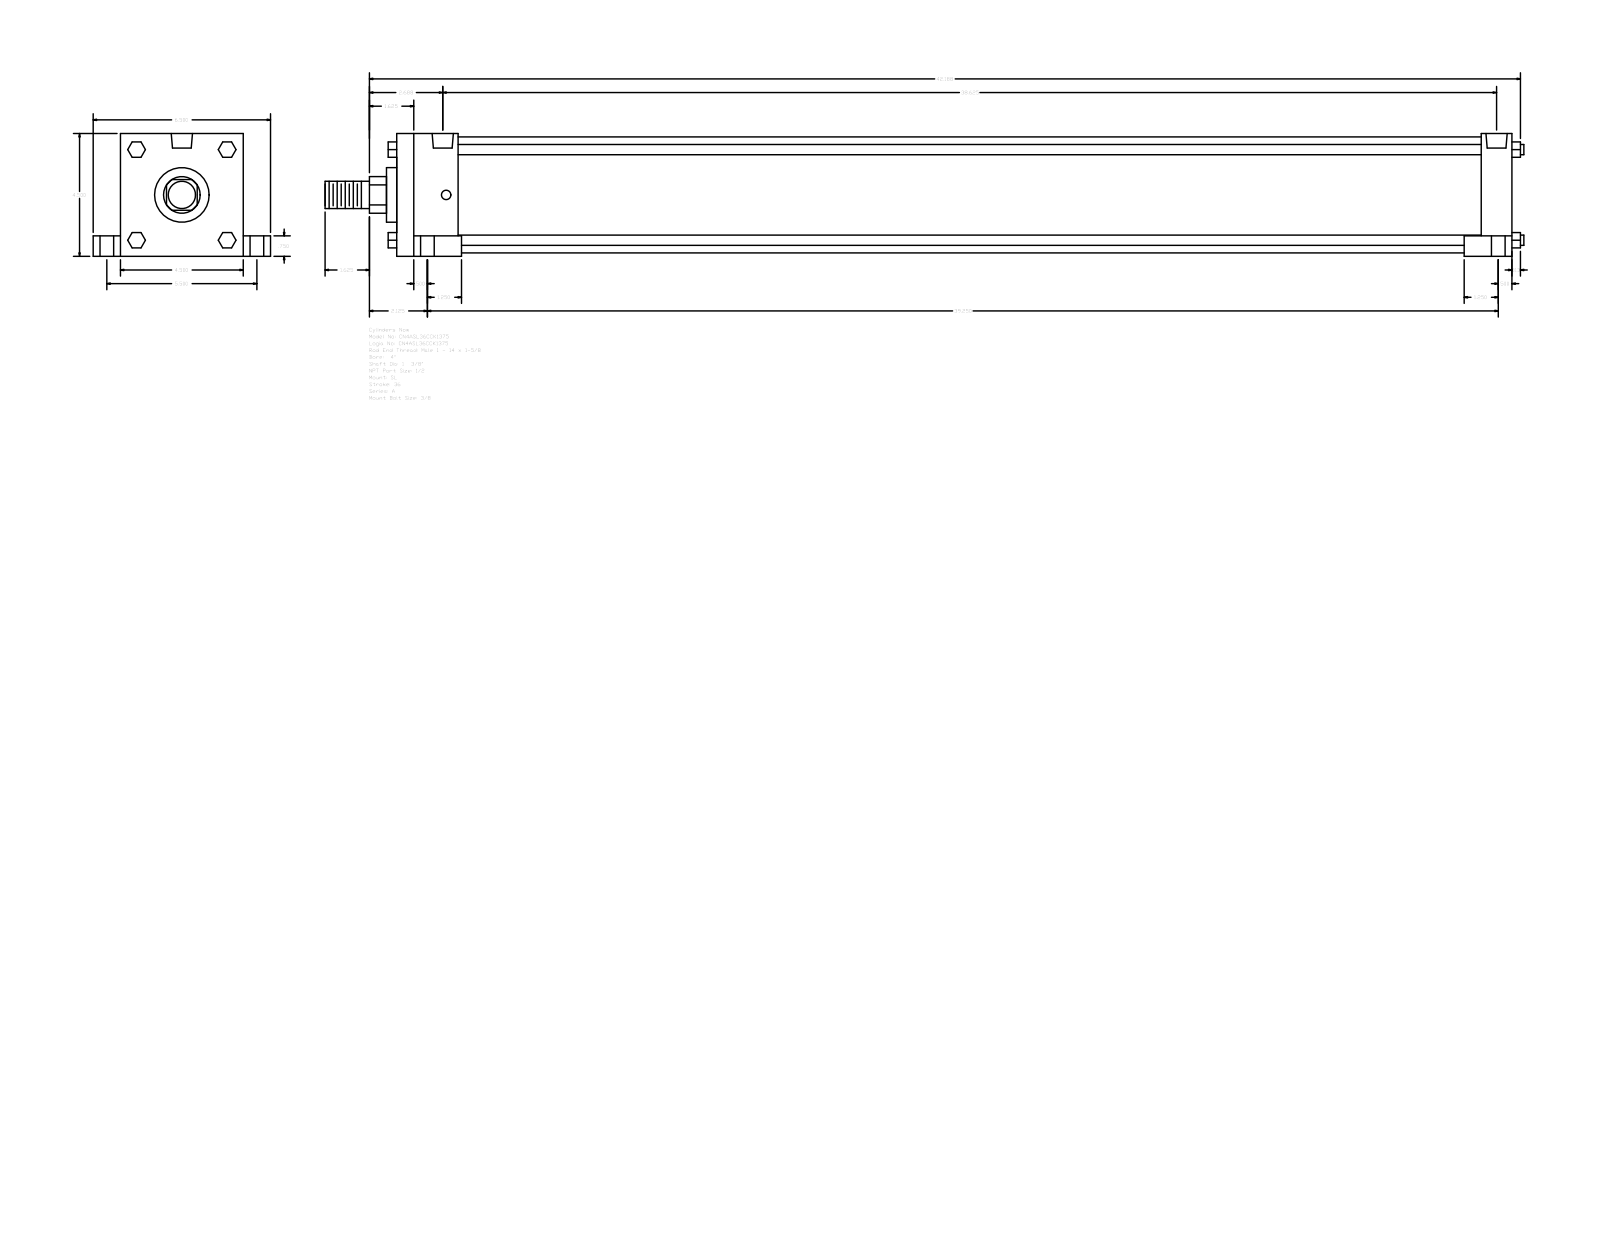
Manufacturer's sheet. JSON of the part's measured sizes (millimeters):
{"part_name": "A_SL__0400_1.375", "step_written_by": "GSSL Pune (CONFIG_CONTROL_DESIGN)", "units": "millimeters", "bodies": {"solids": 0, "faces": 150, "planar": 114, "cylindrical": 36, "other": 0}, "overall_size": [1116.01, 165.1, 114.3], "round_holes": [[8.73, 4], [12.7, 4], [19.05, 4], [19.77, 2]], "round_bosses_or_shafts": [[9.53, 4], [107.95, 1], [50.8, 1], [34.92, 1], [25.4, 1]], "partial_cylinders_radius": [[17.06, 1]], "face_to_face_distances": [114.3, 1038.22, 57.15, 28.57, 25.4, 981.07, 1009.65, 952.5, 139.7, 19.05], "hole_center_spacings": [3.18, 69.87, 70.01, 71.29, 72, 139.7, 974.72, 977.9]}
